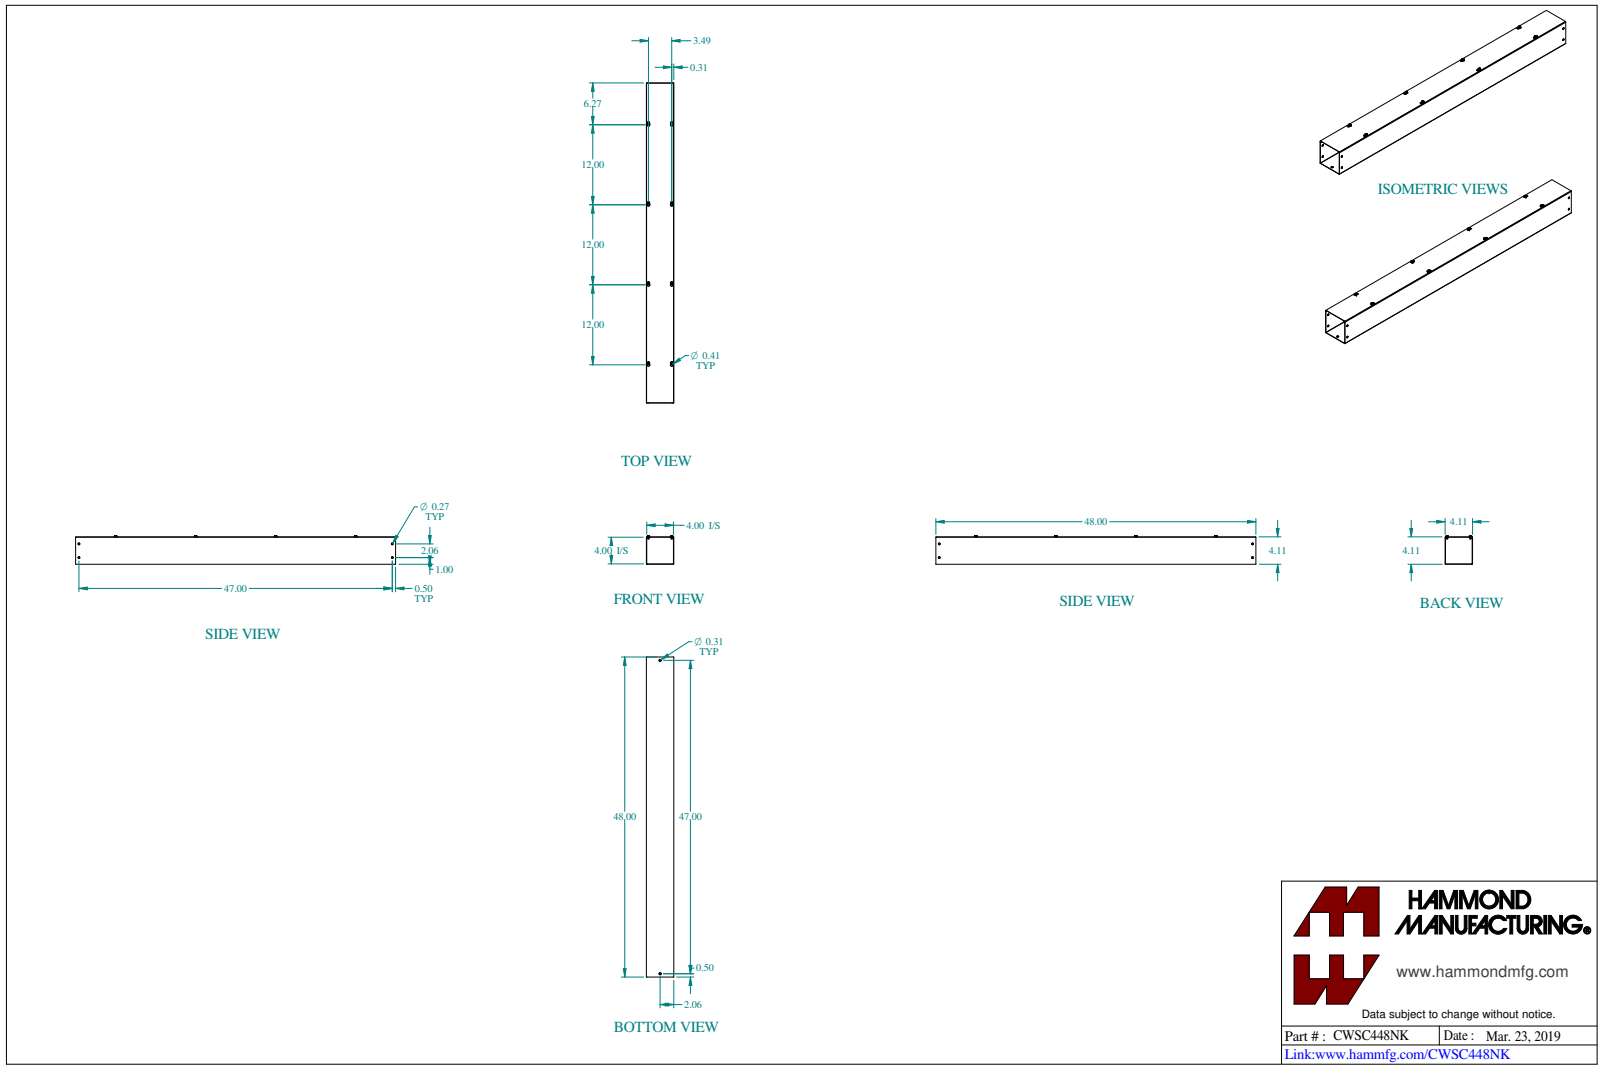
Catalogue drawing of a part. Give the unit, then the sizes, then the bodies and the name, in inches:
Units: inches
Overall size (bounding box): 48 × 4.289 × 4.114
Round holes (diameter × count): ⌀0.177 ×8, ⌀0.266 ×4, ⌀0.313 ×2
Round bosses / shafts (diameter × count): ⌀0.375 ×8, ⌀0.19 ×8
Partial cylindrical surfaces — rounded edges, fillets, slot ends (radius × count): R0.125 ×8, R0.203 ×8, R0.029 ×4, R0.086 ×4
Main face-to-face distances: 0.057, 4.057, 4, 4.114, 3.943, 0.114, 0.031, 4.083, 0.026, 4.026
Hole centre spacings: 12, 12.497, 3.489, 5.77, 17.587, 24, 24.252, 29.552
Volume: 46.38 in³ · Surface area: 1 640 in²
Bodies: 10 solids, 304 faces (148 planar, 108 cylindrical, 48 other)
Part name (STEP PRODUCT): CWSC448NK
STEP written by: SolidWorks 2023 (CONFIG_CONTROL_DESIGN)
